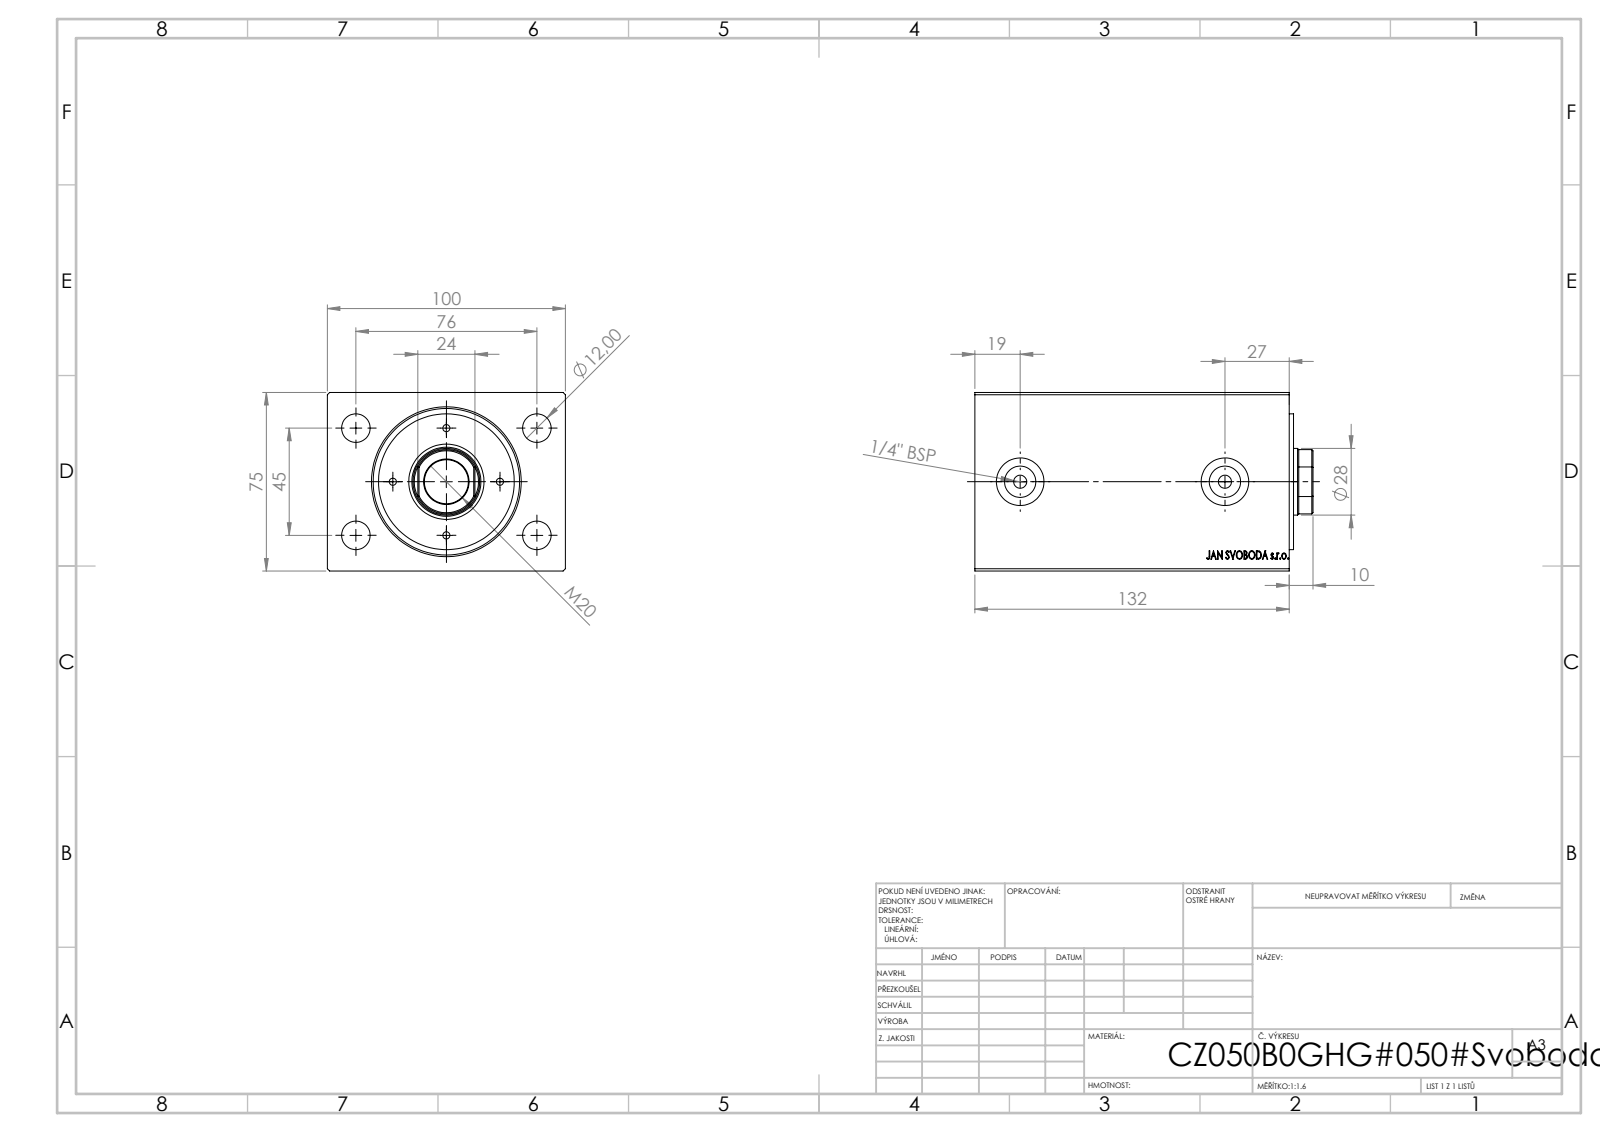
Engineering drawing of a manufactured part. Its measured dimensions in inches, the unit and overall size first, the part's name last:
Units: inches
Overall size (bounding box): 5.591 × 3.937 × 2.953
Round holes (diameter × count): ⌀0.118 ×4, ⌀0.472 ×4, ⌀0.217 ×2, ⌀0.518 ×2, ⌀0.787 ×2, ⌀0.728 ×1, ⌀1.102 ×1, ⌀1.142 ×1, ⌀1.417 ×1, ⌀1.969 ×1, ⌀2.421 ×1
Round bosses / shafts (diameter × count): ⌀2.244 ×1
Partial cylindrical surfaces — rounded edges, fillets, slot ends (radius × count): R0.531 ×1
Main face-to-face distances: 2.953, 3.937, 5.197, 4.496, 0.701, 0.394, 0.071, 0.323, 4.173, 4.874
Hole centre spacings: 0.886, 1.076, 1.253, 1.496, 1.739, 1.772, 2.319, 2.541
Volume: 54.38 in³ · Surface area: 179.5 in²
Bodies: 3 solids, 874 faces (400 planar, 58 cylindrical, 416 other)
Part name (STEP PRODUCT): V500CZ; V500CZ_B_VC
STEP written by: SolidWorks 2019 (CONFIG_CONTROL_DESIGN)
